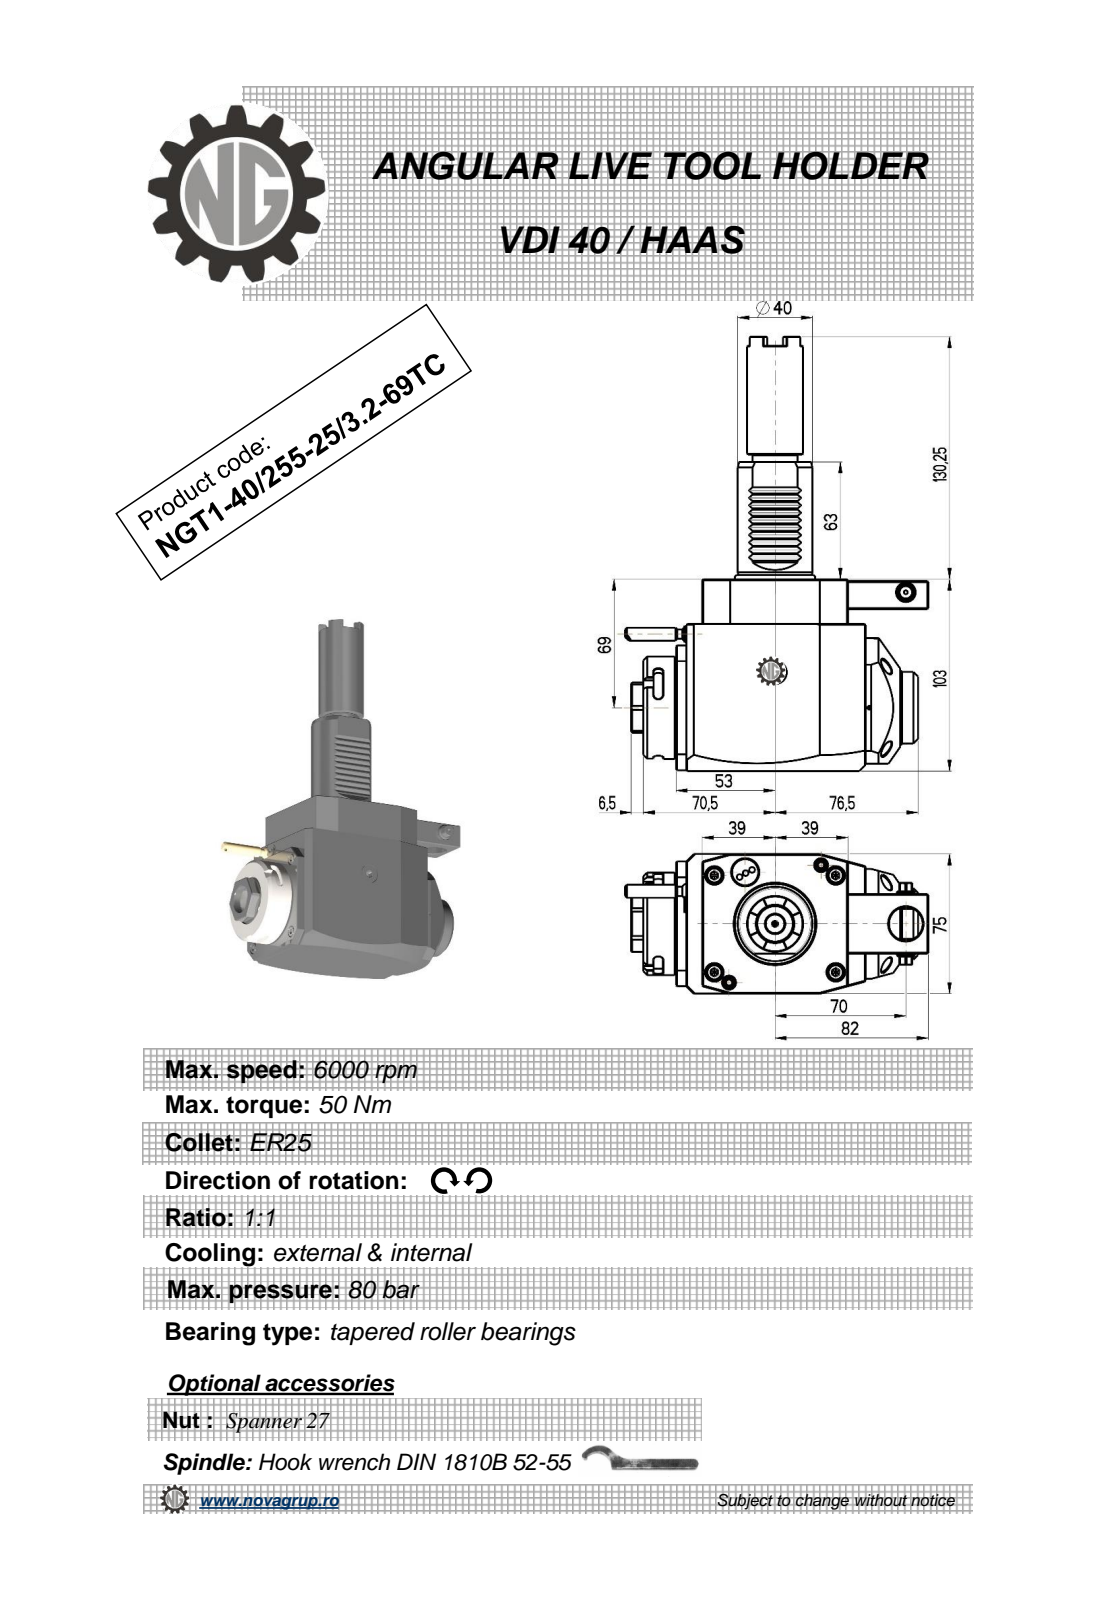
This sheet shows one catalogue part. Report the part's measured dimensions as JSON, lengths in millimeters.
{"part_name": "NGT1_40_255_25_3_2_69TC", "step_written_by": "PRO/ENGINEER BY PARAMETRIC TECHNOLOGY CORPORATION, 2010280 (CONFIG_CONTROL_DESIGN)", "units": "millimeters", "bodies": {"solids": 1, "faces": 391, "planar": 213, "cylindrical": 88, "other": 90}, "overall_size": [233.25, 162.33, 75], "volume_mm3": 951201, "surface_area_mm2": 77501, "round_holes": [[18, 2], [2, 1], [2.5, 1], [3, 1], [9.5, 1], [20, 1]], "round_bosses_or_shafts": [[8.96, 2], [55, 1], [48, 1], [40, 1], [38.5, 1], [30, 1], [24, 1], [10, 1]], "partial_cylinders_radius": [[0.3, 10], [2.5, 6], [180, 2], [0.5, 1], [3.85, 1], [4.25, 1], [15, 1], [24.5, 1]], "face_to_face_distances": [75, 103, 17.5, 23, 79, 102, 24, 31.5, 14, 87], "hole_center_spacings": [28.11, 43.2, 61.5, 70]}
